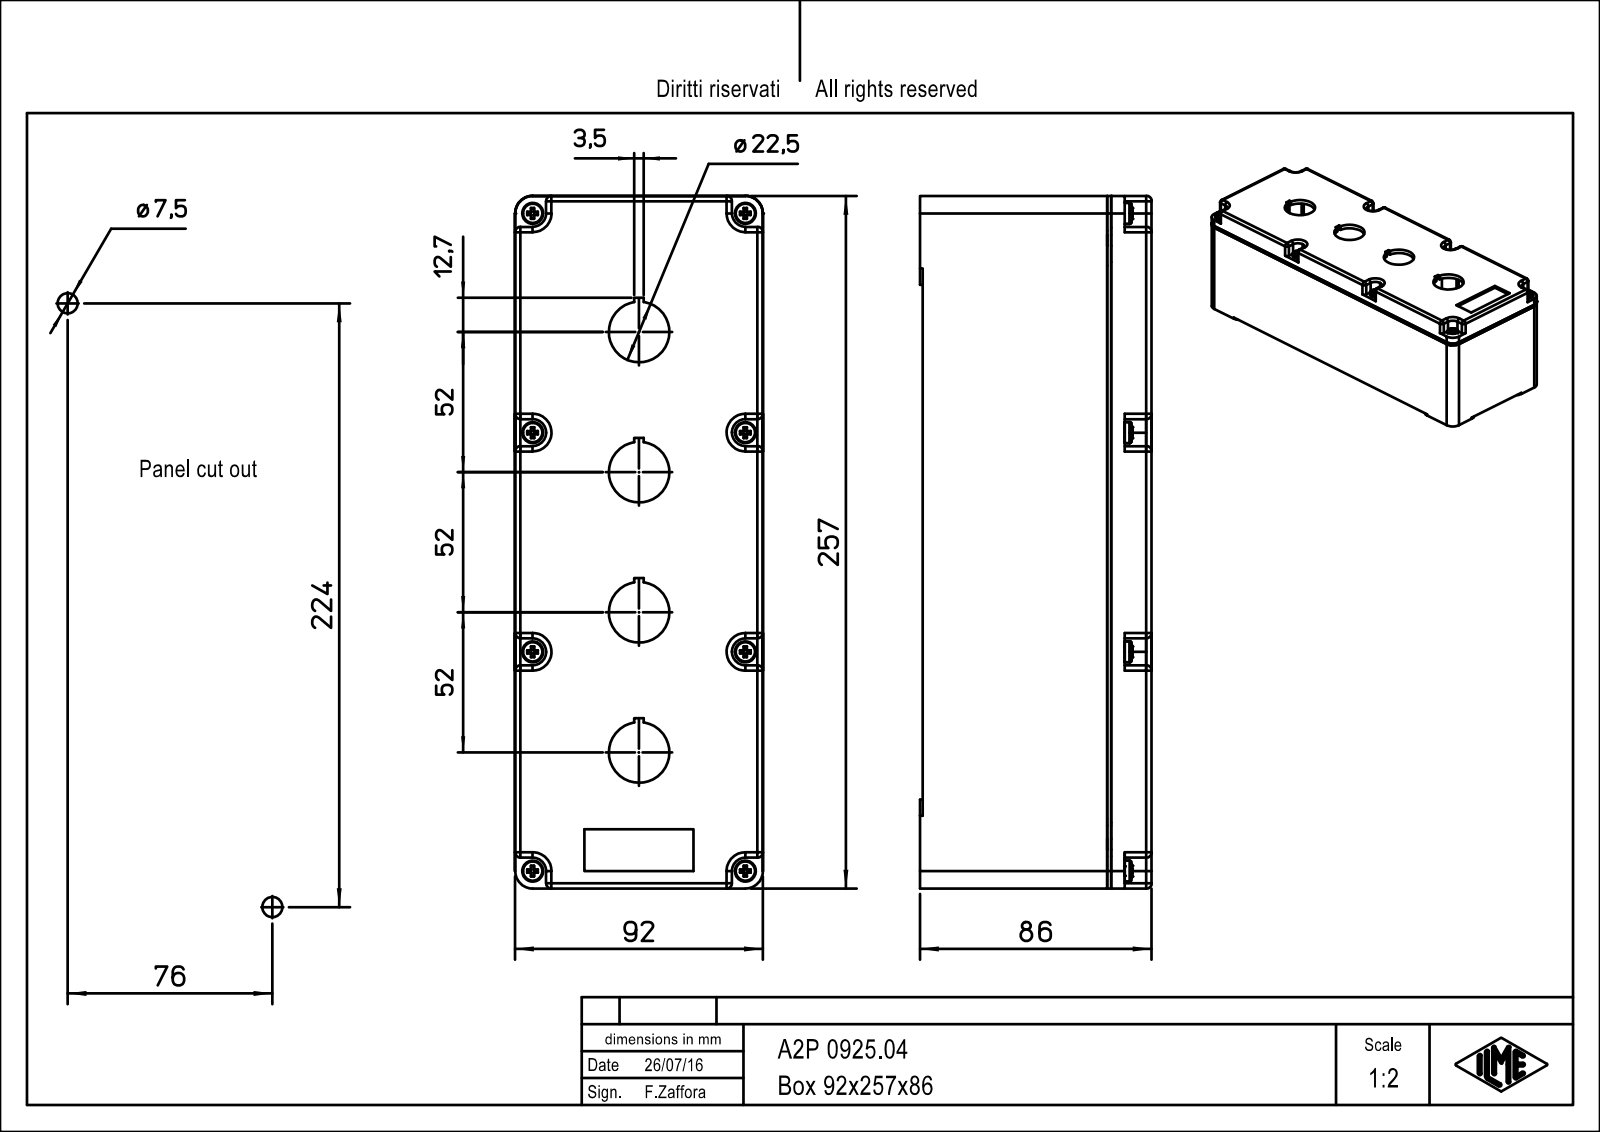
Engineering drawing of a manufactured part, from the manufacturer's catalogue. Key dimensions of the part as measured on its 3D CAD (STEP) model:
Part name (STEP PRODUCT): BOX; COVER; A2P_0925.04
STEP written by: PTC Creo Elements/Direct Modeling 19.0B 21-Mar-2015 (C) Parametric Technology GmbH (AUTOMOTIVE_DESIGN)
Units: millimetres
Bodies: 2 solids, 1288 faces (927 planar, 293 cylindrical, 68 other)
Overall size (bounding box): 257 × 92.02 × 86
Volume: 434 611 mm³ · Surface area: 236 582 mm²
Round holes (diameter × count): ⌀3.3 ×10, ⌀4.5 ×8, ⌀5 ×8, ⌀6 ×8, ⌀22.5 ×4, ⌀5.8 ×2, ⌀7.5 ×2, ⌀10.6 ×1, ⌀10.61 ×1
Round bosses / shafts (diameter × count): ⌀7.8 ×8, ⌀4 ×8, ⌀6.2 ×2, ⌀6 ×2, ⌀7 ×1
Partial cylindrical surfaces — rounded edges, fillets, slot ends (radius × count): R2 ×29, R0.33 ×22, R6 ×12, R6.5 ×12, R5 ×10, R8 ×10, R6.37 ×6, R0.27 ×4
Main face-to-face distances: 3, 82, 92, 85, 79, 4.38, 4.37, 87.63, 87.62, 83.25
Hole centre spacings: 79, 113.4, 42.13, 81.35, 162.65, 180.82, 54.36, 77.48
